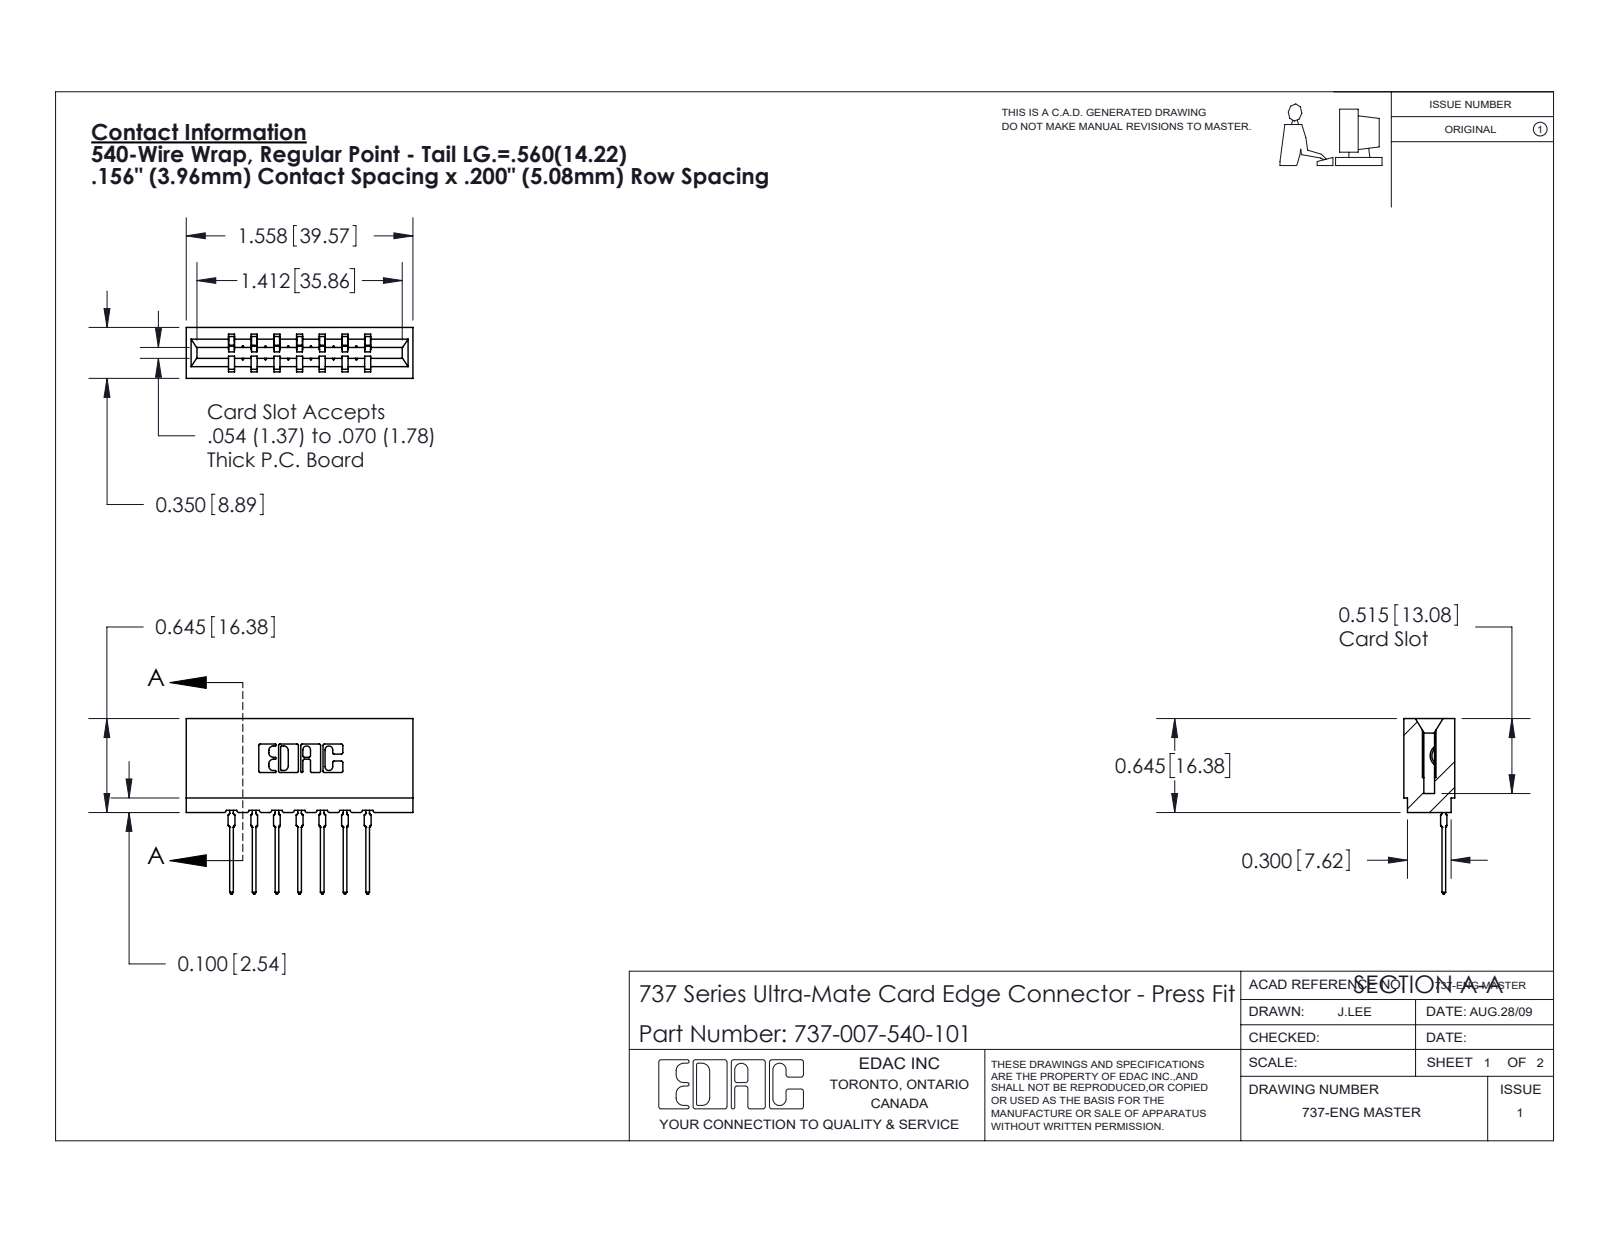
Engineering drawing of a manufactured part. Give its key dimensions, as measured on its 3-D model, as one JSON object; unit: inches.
{"part_name": "745-292-001_540; 737 Part_Insulator Option - 01; 737-007-540-101", "step_written_by": "SolidWorks 2020 (CONFIG_CONTROL_DESIGN)", "units": "inches", "bodies": {"solids": 8, "faces": 885, "planar": 530, "cylindrical": 173, "other": 182}, "overall_size": [1.558, 1.206, 0.35], "volume_in3": 0.249, "surface_area_in2": 7.634, "partial_cylinders_radius": [[0.01, 22], [0.015, 14], [0.021, 14], [0.007, 6], [0.031, 6], [0.005, 4], [0.011, 4], [0.026, 3]], "face_to_face_distances": [0.156, 0.138, 0.212, 0.35, 0.312, 0.354, 0.198, 0.624, 0.468, 0.074]}
